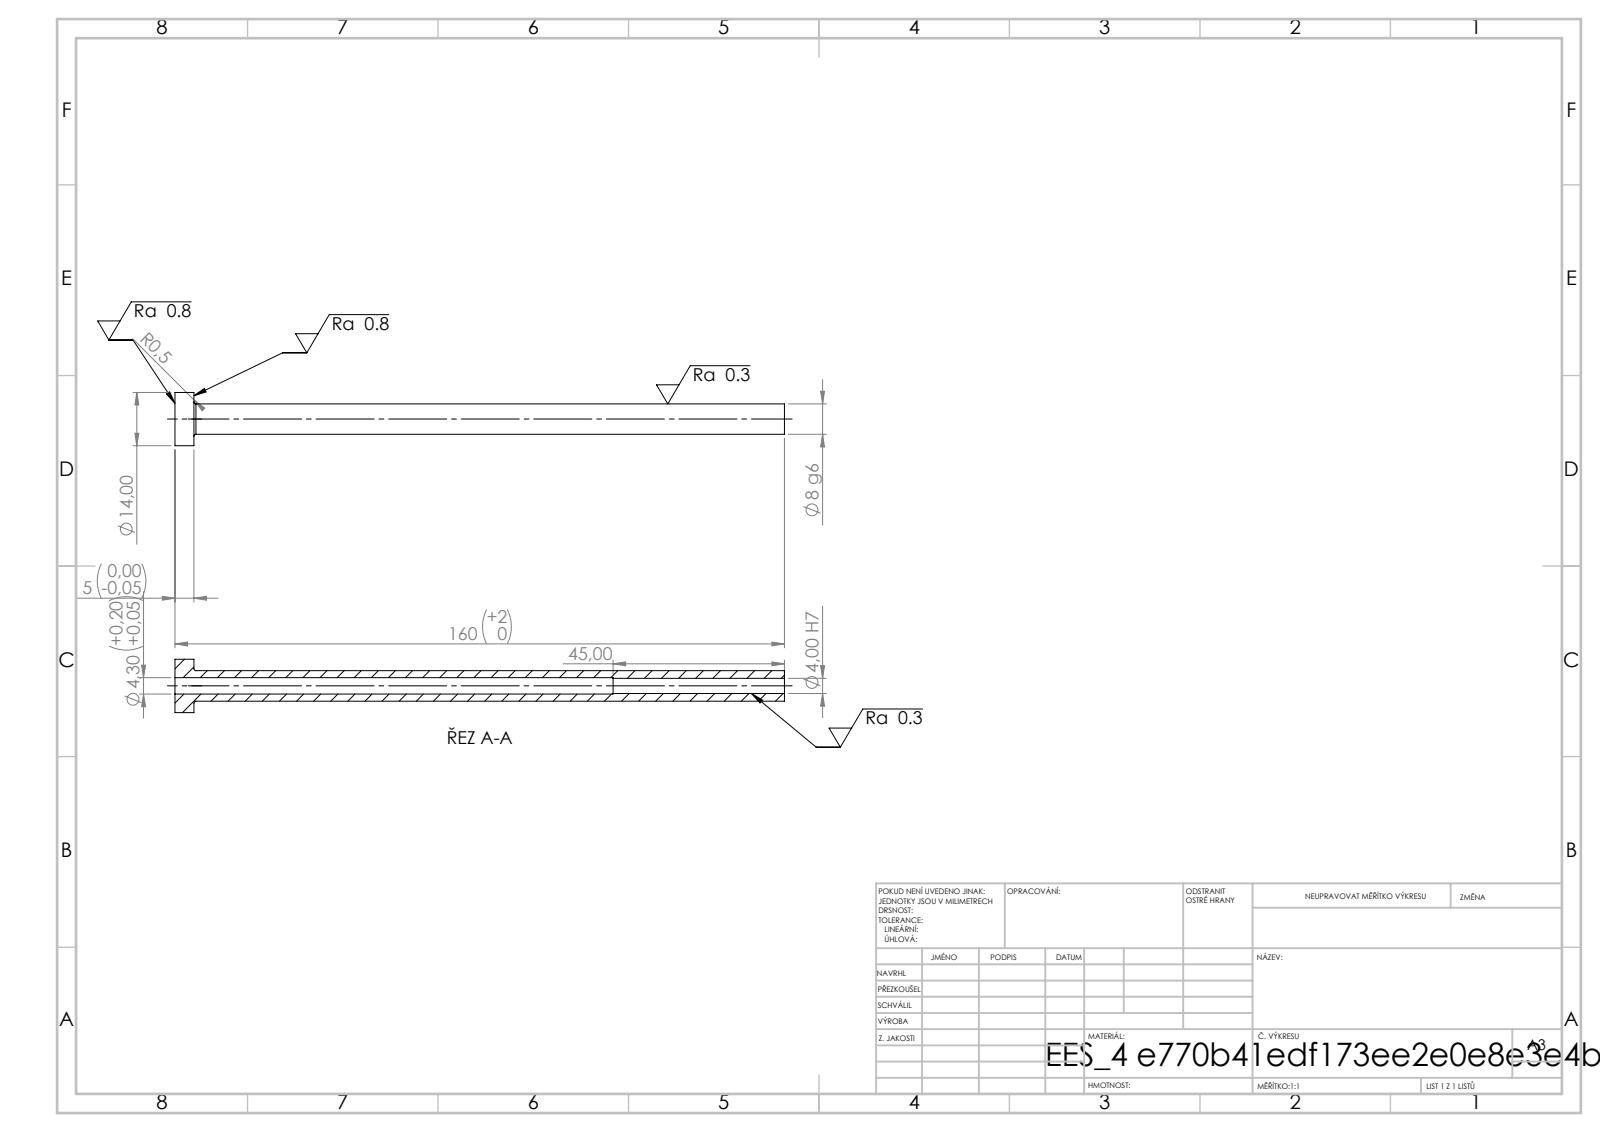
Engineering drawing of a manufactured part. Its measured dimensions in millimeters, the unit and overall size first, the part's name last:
Units: millimetres
Overall size (bounding box): 160 × 14 × 14
Round holes (diameter × count): ⌀4 ×1, ⌀4.3 ×1
Round bosses / shafts (diameter × count): ⌀14 ×1, ⌀8 ×1
Main face-to-face distances: 5, 160, 155, 115, 110, 45
Volume: 6 327 mm³ · Surface area: 6 512 mm²
Bodies: 1 solid, 14 faces (4 planar, 8 cylindrical, 2 other)
STEP written by: SolidWorks 2019 (CONFIG_CONTROL_DESIGN)
